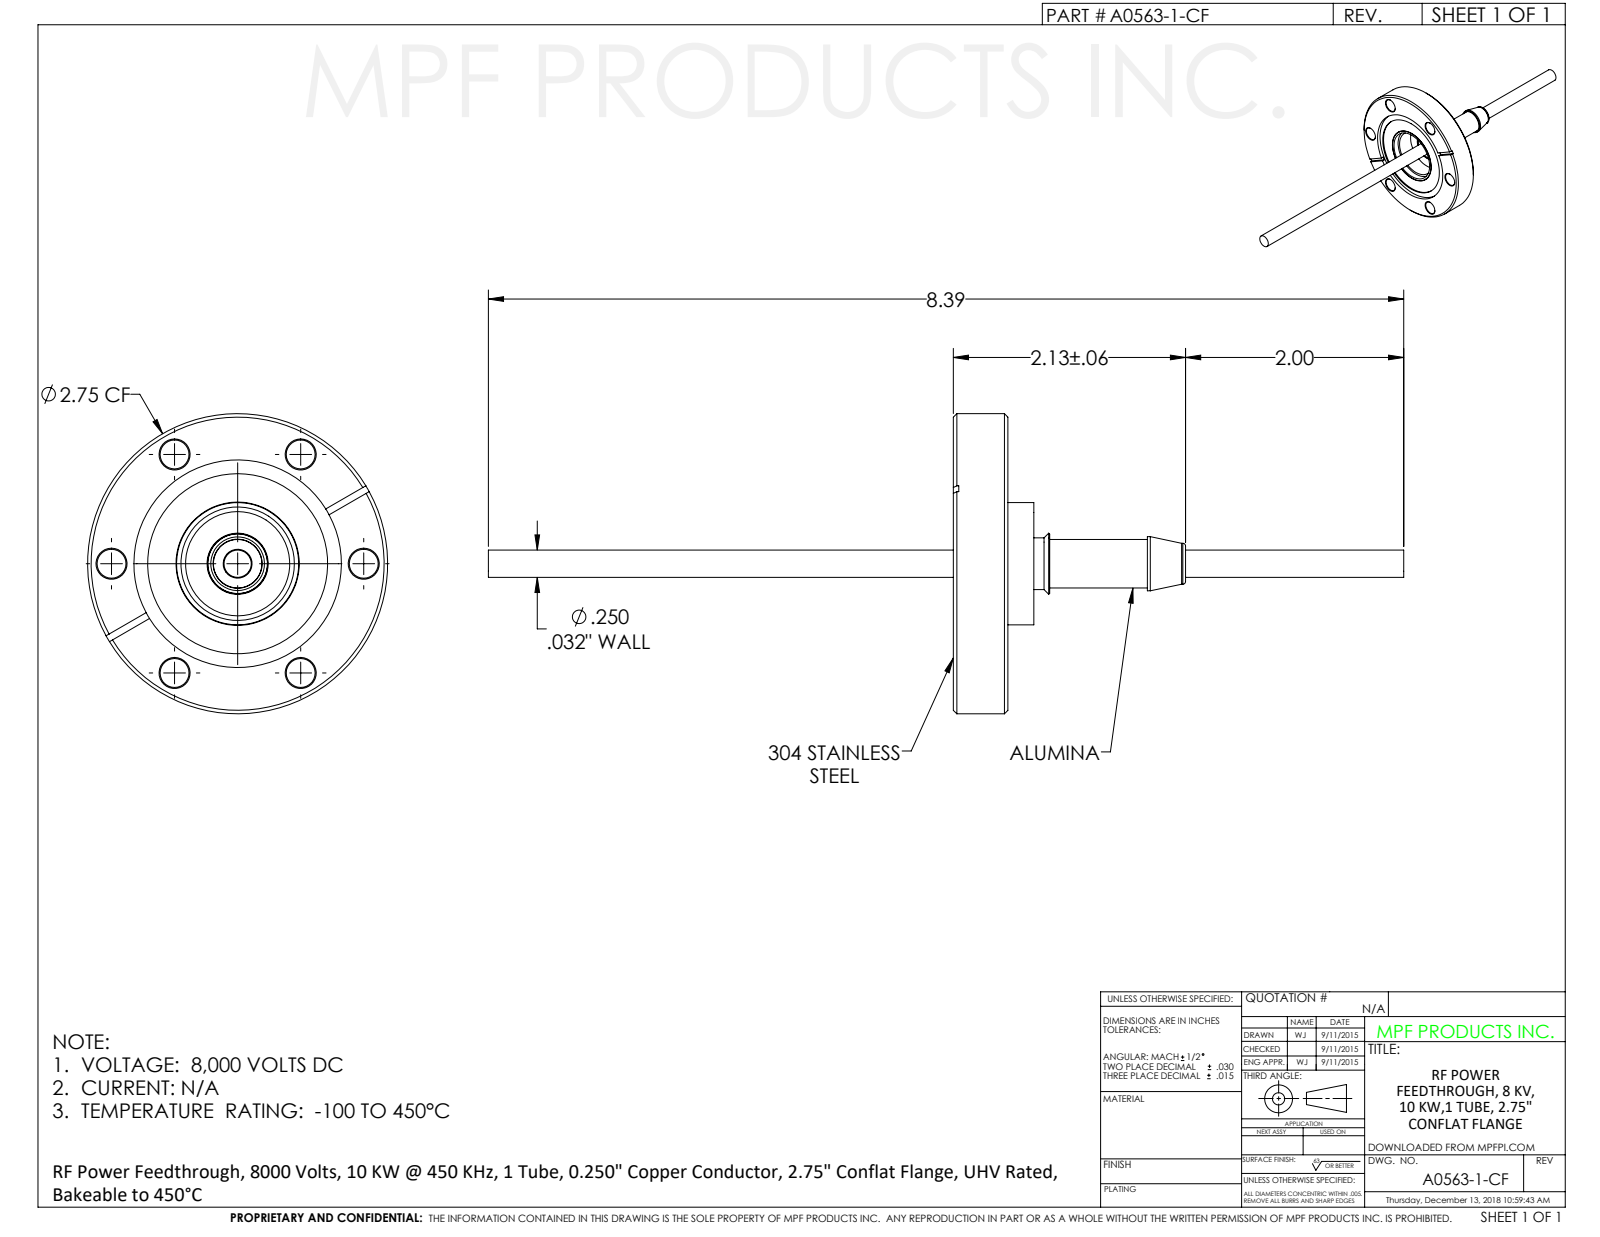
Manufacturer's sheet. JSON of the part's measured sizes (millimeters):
{"part_name": "A0563-1-CF", "step_written_by": "SolidWorks 2012 (CONFIG_CONTROL_DESIGN)", "units": "millimeters", "bodies": {"solids": 1, "faces": 105, "planar": 17, "cylindrical": 52, "other": 36}, "overall_size": [213.1, 69.9, 69.9], "volume_mm3": 46720, "surface_area_mm2": 24160, "round_holes": [[6.7, 4], [6.7, 3], [4.7, 1], [12.5, 1], [14, 1], [24.3, 1], [25.4, 1], [26.4, 1], [41.9, 1], [48.3, 1]], "round_bosses_or_shafts": [[69.9, 1], [28.4, 1], [14.5, 1], [14.1, 1], [12.6, 1], [12, 1], [11.3, 1], [6.4, 1]], "face_to_face_distances": [12.7, 1.3, 11.4, 15.6, 14.4, 2.9, 3.2, 12.5, 11.2, 8.4], "hole_center_spacings": [29.4, 50.9, 50.9, 58.7, 58.7]}
